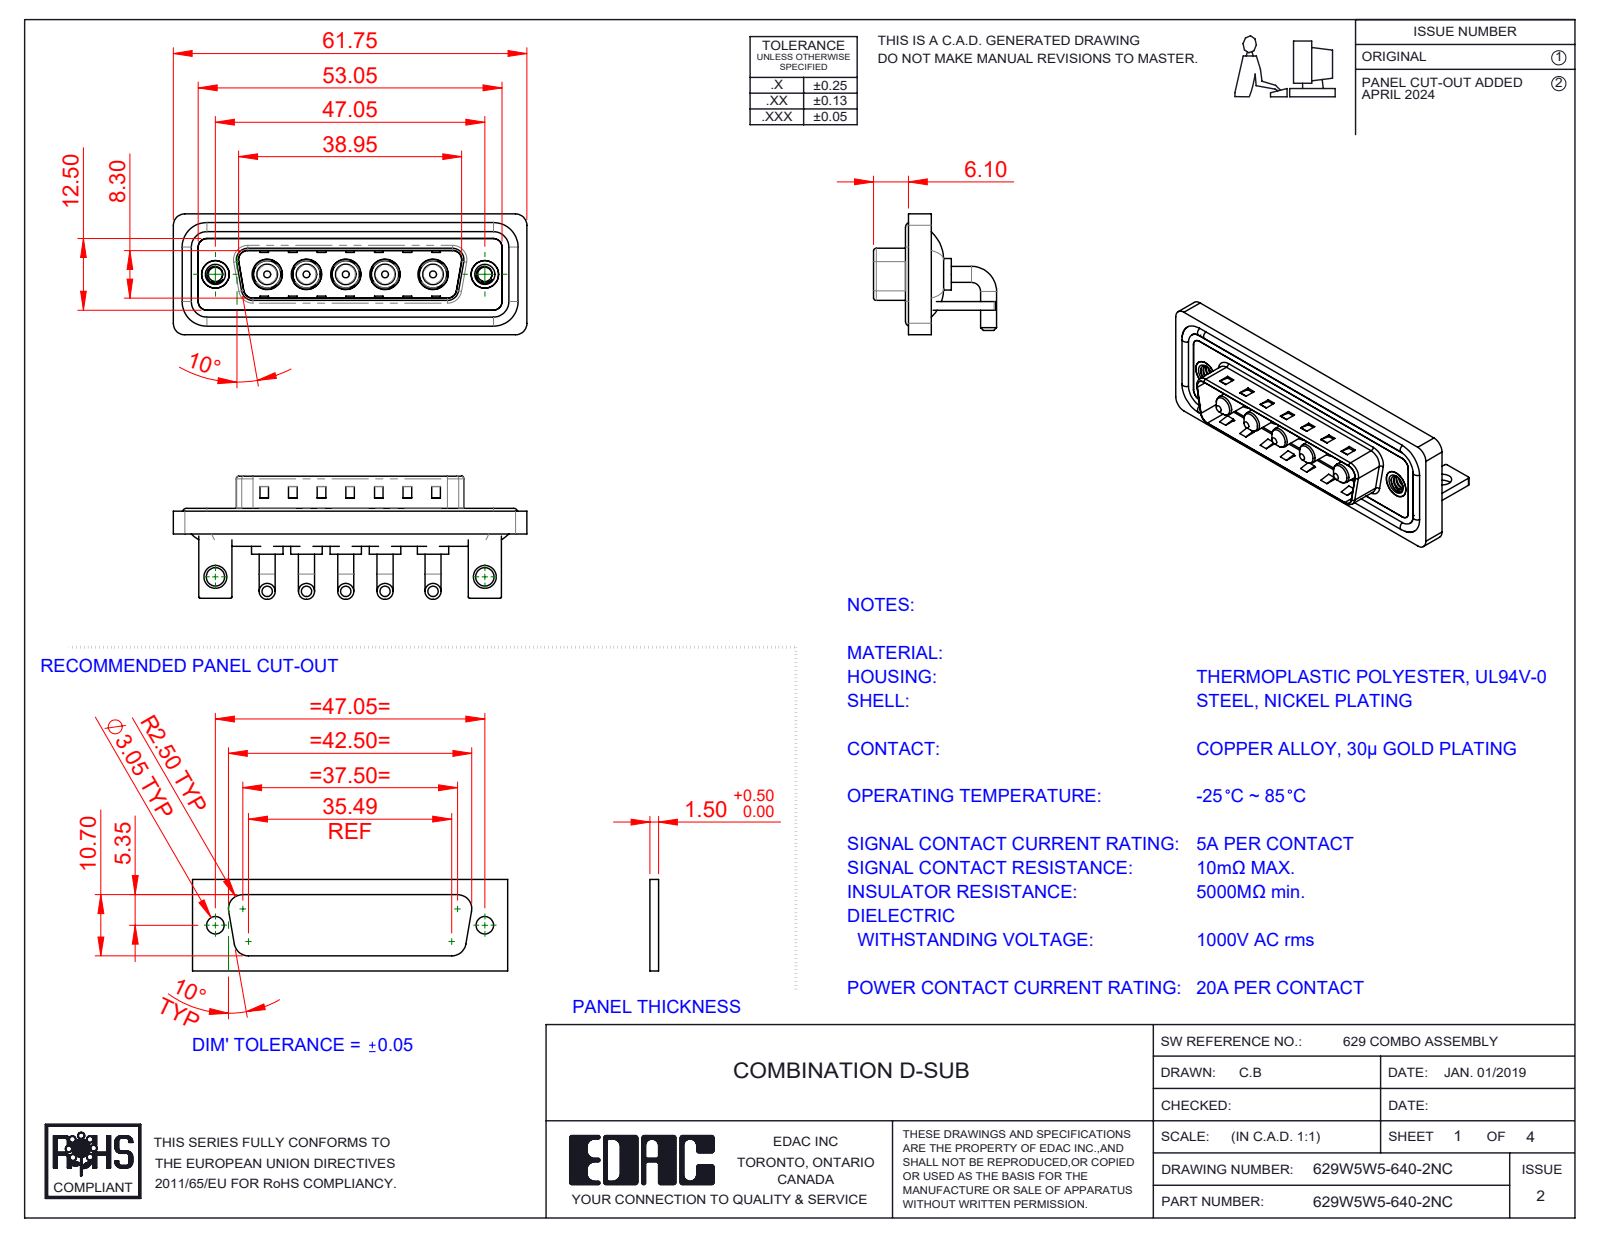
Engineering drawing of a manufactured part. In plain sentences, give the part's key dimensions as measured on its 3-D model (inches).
The part is named "629W5W5-640-2NC; 629Combo Shell Front_25 Contacts; Power Pin_20A RA; 629Combo Stabilizer Bracket (+4 more)". Its 3-D file was written by "SolidWorks 2023 (CONFIG_CONTROL_DESIGN)". It is 19 solids with 736 faces: 279 planar, 311 cylindrical and 146 other. Overall it measures 2.431 by 0.846 by 0.831 inches. Its volume is 0.493 cubic inches and its surface area 19.93 square inches. Round holes: 5 of diameter 0.191, 5 of diameter 0.209, 2 of diameter 0.098, 2 of diameter 0.126, 2 of diameter 0.157, 2 of diameter 0.189, 2 of diameter 0.197. Round bosses or shafts: 10 of diameter 0.11, 5 of diameter 0.217, 5 of diameter 0.205, 5 of diameter 0.187, 5 of diameter 0.148, 5 of diameter 0.142, 4 of diameter 0.063, 2 of diameter 0.193. Partial cylindrical surfaces (rounded edges, fillets, slot ends): 19 of radius 0.079, 18 of radius 0.059, 16 of radius 0.01, 9 of radius 0.02, 8 of radius 0.063, 5 of radius 0.083, 4 of radius 0.024, 4 of radius 0.026. The main face-to-face distances are 0.016, 0.059, 0.114, 0.031, 0.083, 0.146, 0.043, 0.177, 0.161, 0.047. The hole center spacings are 0.27, 0.541, 1.852, 0.27, 0.27, 0.33, 0.33, 0.356.
